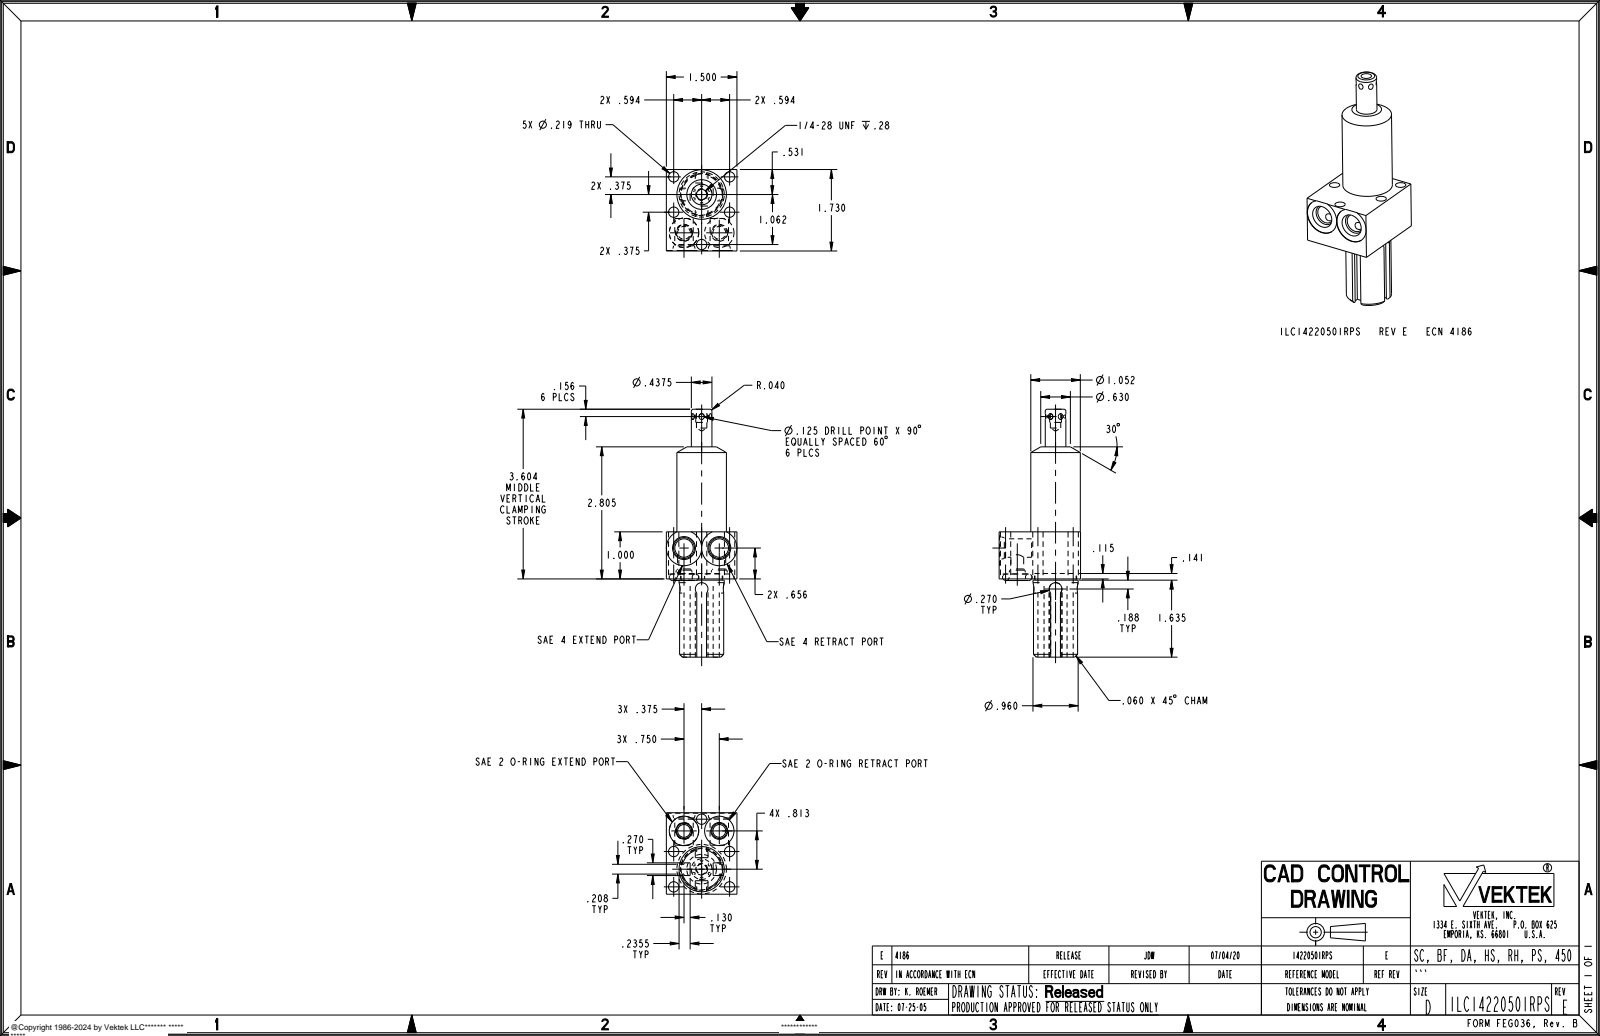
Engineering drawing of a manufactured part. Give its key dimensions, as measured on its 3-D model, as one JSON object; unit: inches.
{"part_name": "ILC14220501RPS", "step_written_by": "PRO/ENGINEER BY PARAMETRIC TECHNOLOGY CORPORATION, 2013320 (AUTOMOTIVE_DESIGN)", "units": "inches", "bodies": {"solids": 2, "faces": 133, "planar": 49, "cylindrical": 42, "other": 42}, "overall_size": [5.265, 1.73, 1.5], "volume_in3": 4.606, "surface_area_in2": 34.33, "round_holes": [[0.219, 5], [0.272, 2], [0.392, 2], [0.625, 2], [0.75, 2], [0.221, 1], [0.895, 1]], "round_bosses_or_shafts": [[1.052, 1], [0.96, 1], [0.875, 1], [0.437, 1], [0.25, 1]], "partial_cylinders_radius": [[0.135, 2]], "face_to_face_distances": [1.5, 0.109, 0.38, 1, 0.141, 0.348, 0.031, 0.239, 0.506, 0.994], "hole_center_spacings": [0.702, 0.75, 0.45, 0.49, 0.895, 0.908, 1.063, 1.188]}
